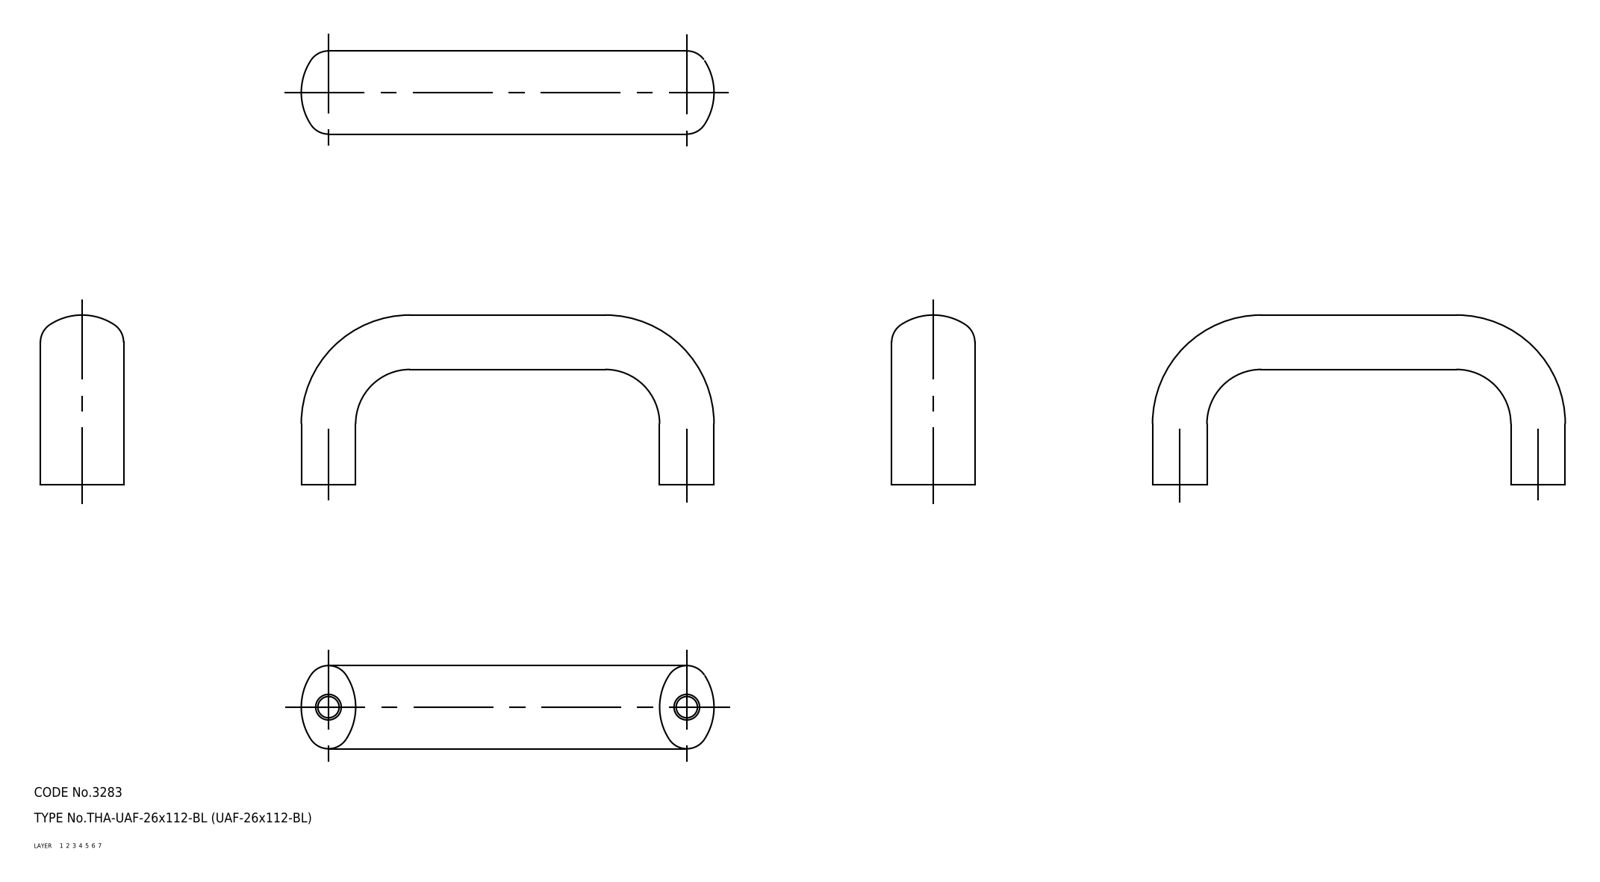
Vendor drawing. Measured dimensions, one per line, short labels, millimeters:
name: pull
written by: CADfix (AUTOMOTIVE_DESIGN)
unit: mm
bodies: 1 solid, 18 faces (0 planar, 0 cylindrical, 18 other)
size: 129 × 53 × 26
volume: 60 931 mm³; area: 13 526 mm²
